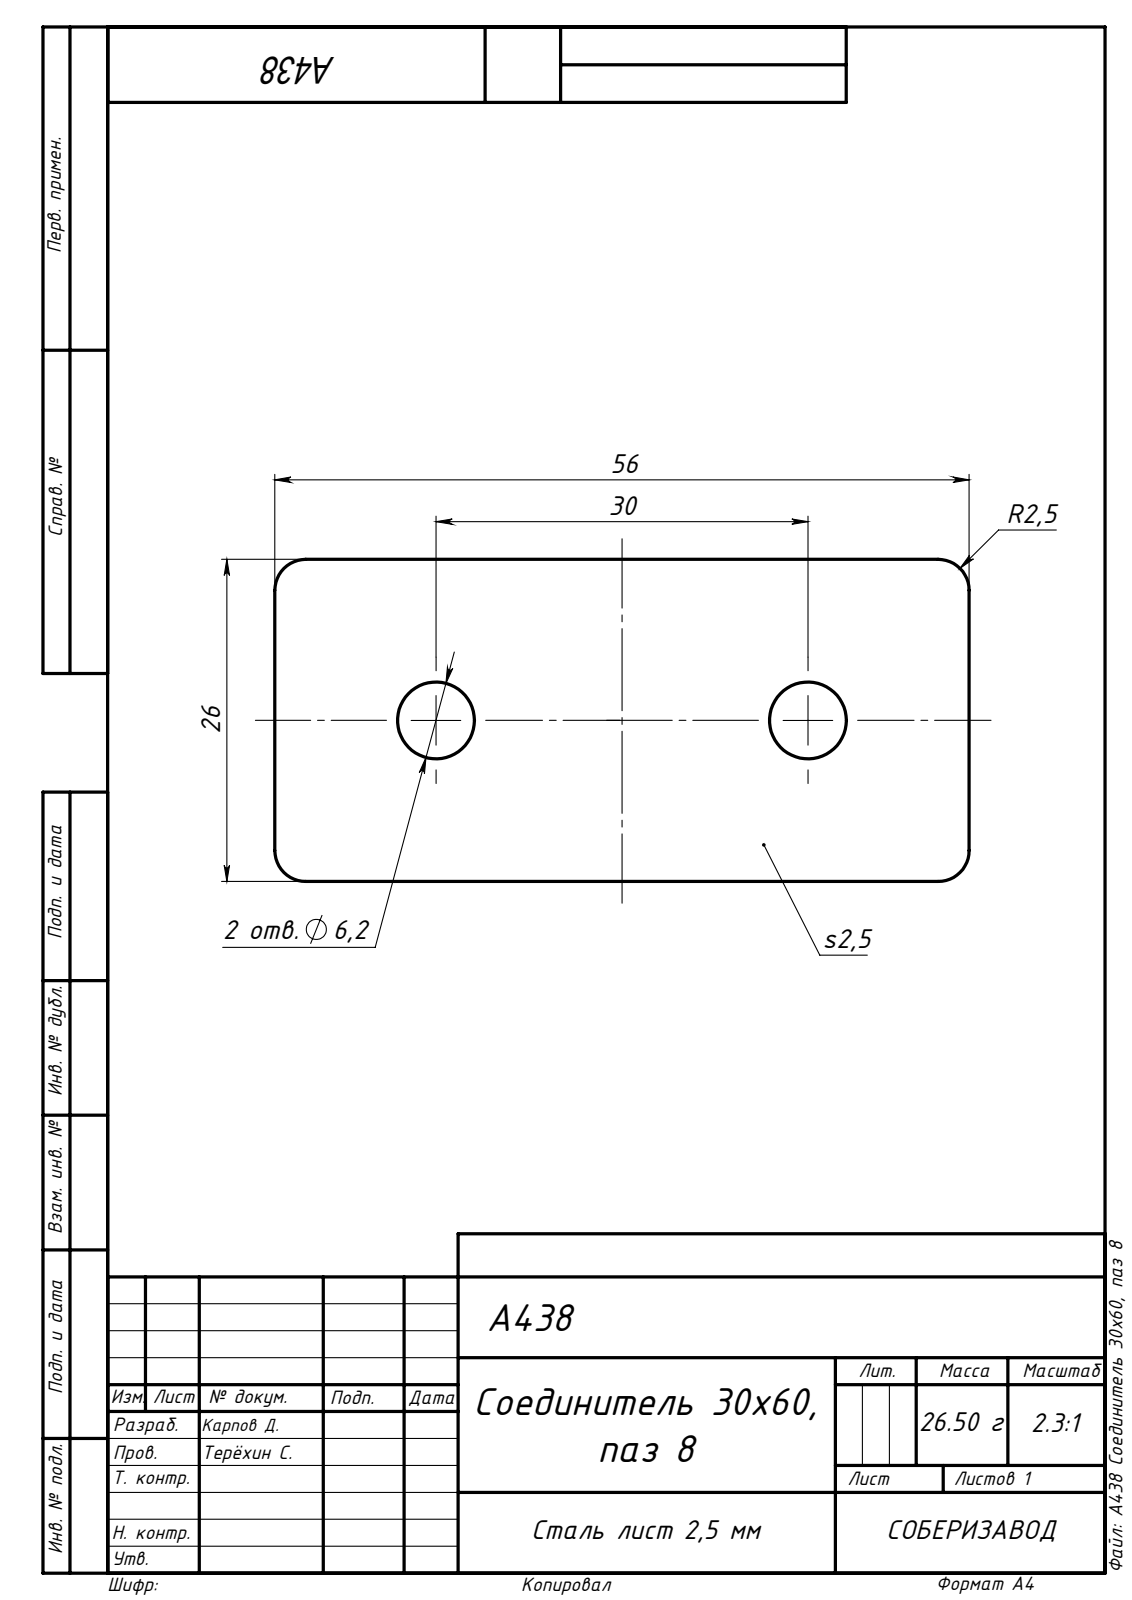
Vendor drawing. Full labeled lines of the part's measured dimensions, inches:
STEP written by: SolidWorks 2020 (AUTOMOTIVE_DESIGN)
Units: inches
Bodies: 1 solid, 14 faces (6 planar, 8 cylindrical, 0 other)
Overall size (bounding box): 2.205 × 1.024 × 0.098
Volume: 0.212 in³ · Surface area: 5.079 in²
Round holes (diameter × count): ⌀0.244 ×2
Partial cylindrical surfaces — rounded edges, fillets, slot ends (radius × count): R0.098 ×4
Main face-to-face distances: 0.098, 1.024, 2.205
Hole centre spacings: 1.181
